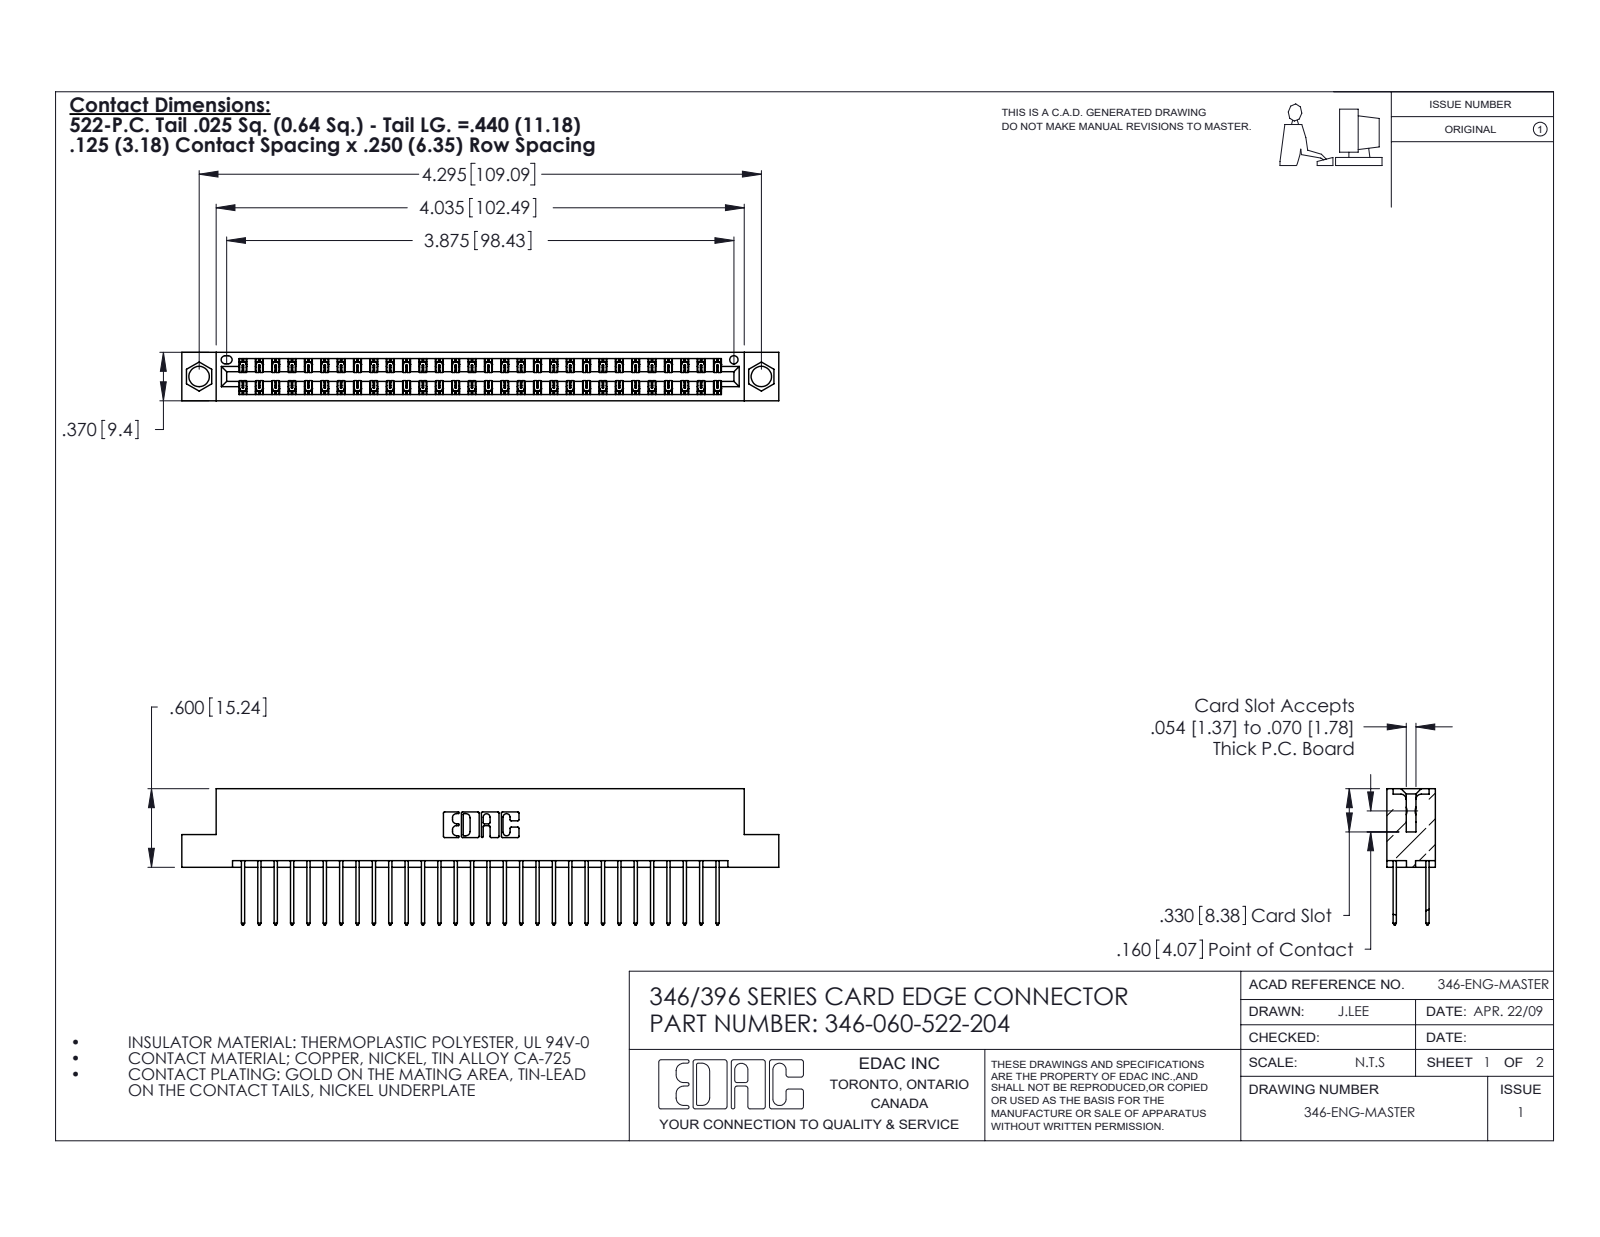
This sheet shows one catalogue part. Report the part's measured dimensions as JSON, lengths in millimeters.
{"part_name": "346-060-522-204; 346 Part_Flush Mounting Lugs - 0.156 Dia-TH; 345-292-001_345-293-122", "step_written_by": "SolidWorks 2020 (CONFIG_CONTROL_DESIGN)", "units": "millimeters", "bodies": {"solids": 61, "faces": 3256, "planar": 2190, "cylindrical": 1066, "other": 0}, "overall_size": [115.8, 26.4, 9.4], "volume_mm3": 11200, "surface_area_mm2": 15830, "round_holes": [[4, 2], [1.6, 1]], "partial_cylinders_radius": [[0.2, 90], [0.3, 60], [0.3, 22], [0.2, 6], [0.8, 6], [0.7, 3], [0.4, 2], [0.6, 2]], "face_to_face_distances": [1.2, 8.2, 6.4, 9.4, 1.8, 7.6, 0.6, 7, 3.8, 5.6], "hole_center_spacings": [6.2, 103.8, 109.1]}
